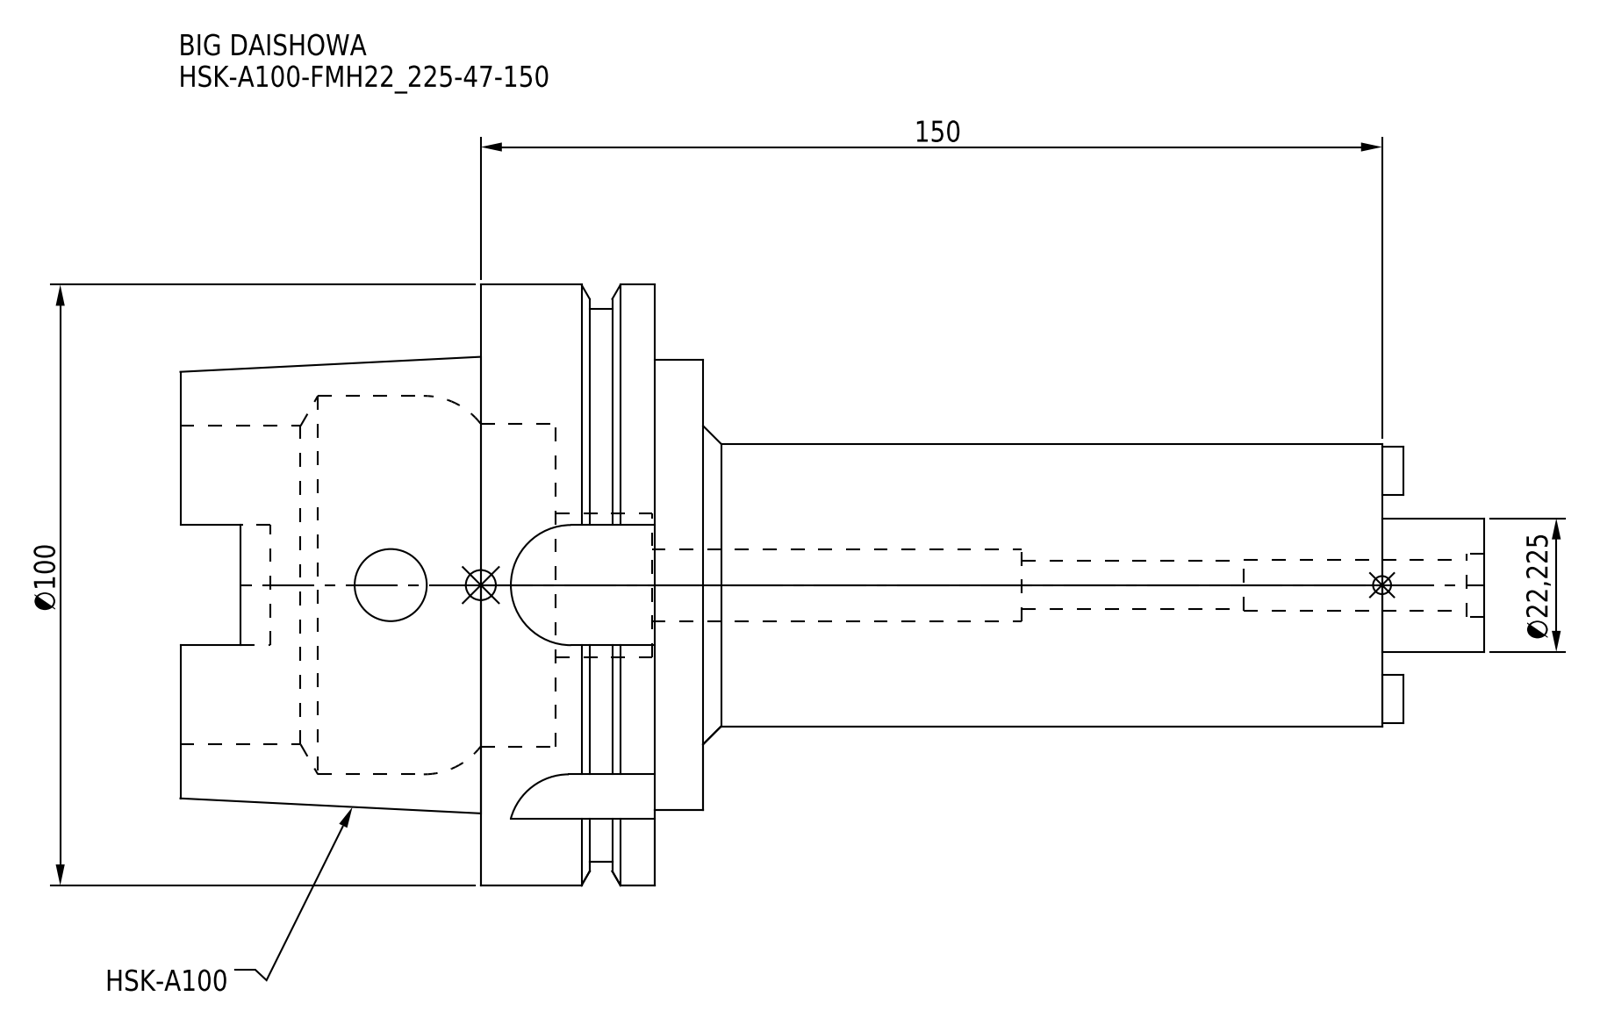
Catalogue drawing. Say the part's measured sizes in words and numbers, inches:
The part is named "HSK-A100-FMH22_225-47-150". Its 3-D file was written by "CREO PARAMETRIC BY PTC INC, 2016380 (AUTOMOTIVE_DESIGN)". It is 1 solid with 109 faces: 47 planar, 46 cylindrical and 16 other. Overall it measures 8.543 by 3.937 by 3.937 inches. Its volume is 29.38 cubic inches and its surface area 114.6 square inches. Round holes: 2 of diameter 0.472, 1 of diameter 0.315, 1 of diameter 0.335, 1 of diameter 0.413, 1 of diameter 0.945, 1 of diameter 2.087, 1 of diameter 2.118, 1 of diameter 2.48. Round bosses or shafts: 1 of diameter 3.937, 1 of diameter 3.622, 1 of diameter 2.953, 1 of diameter 1.85, 1 of diameter 0.875. Partial cylindrical surfaces (rounded edges, fillets, slot ends): 4 of radius 0.192, 4 of radius 0.394. The main face-to-face distances are 1.142, 0.315, 1.457, 0.967, 0.652, 0.49, 4.449, 4.764, 5.415, 5.906.
